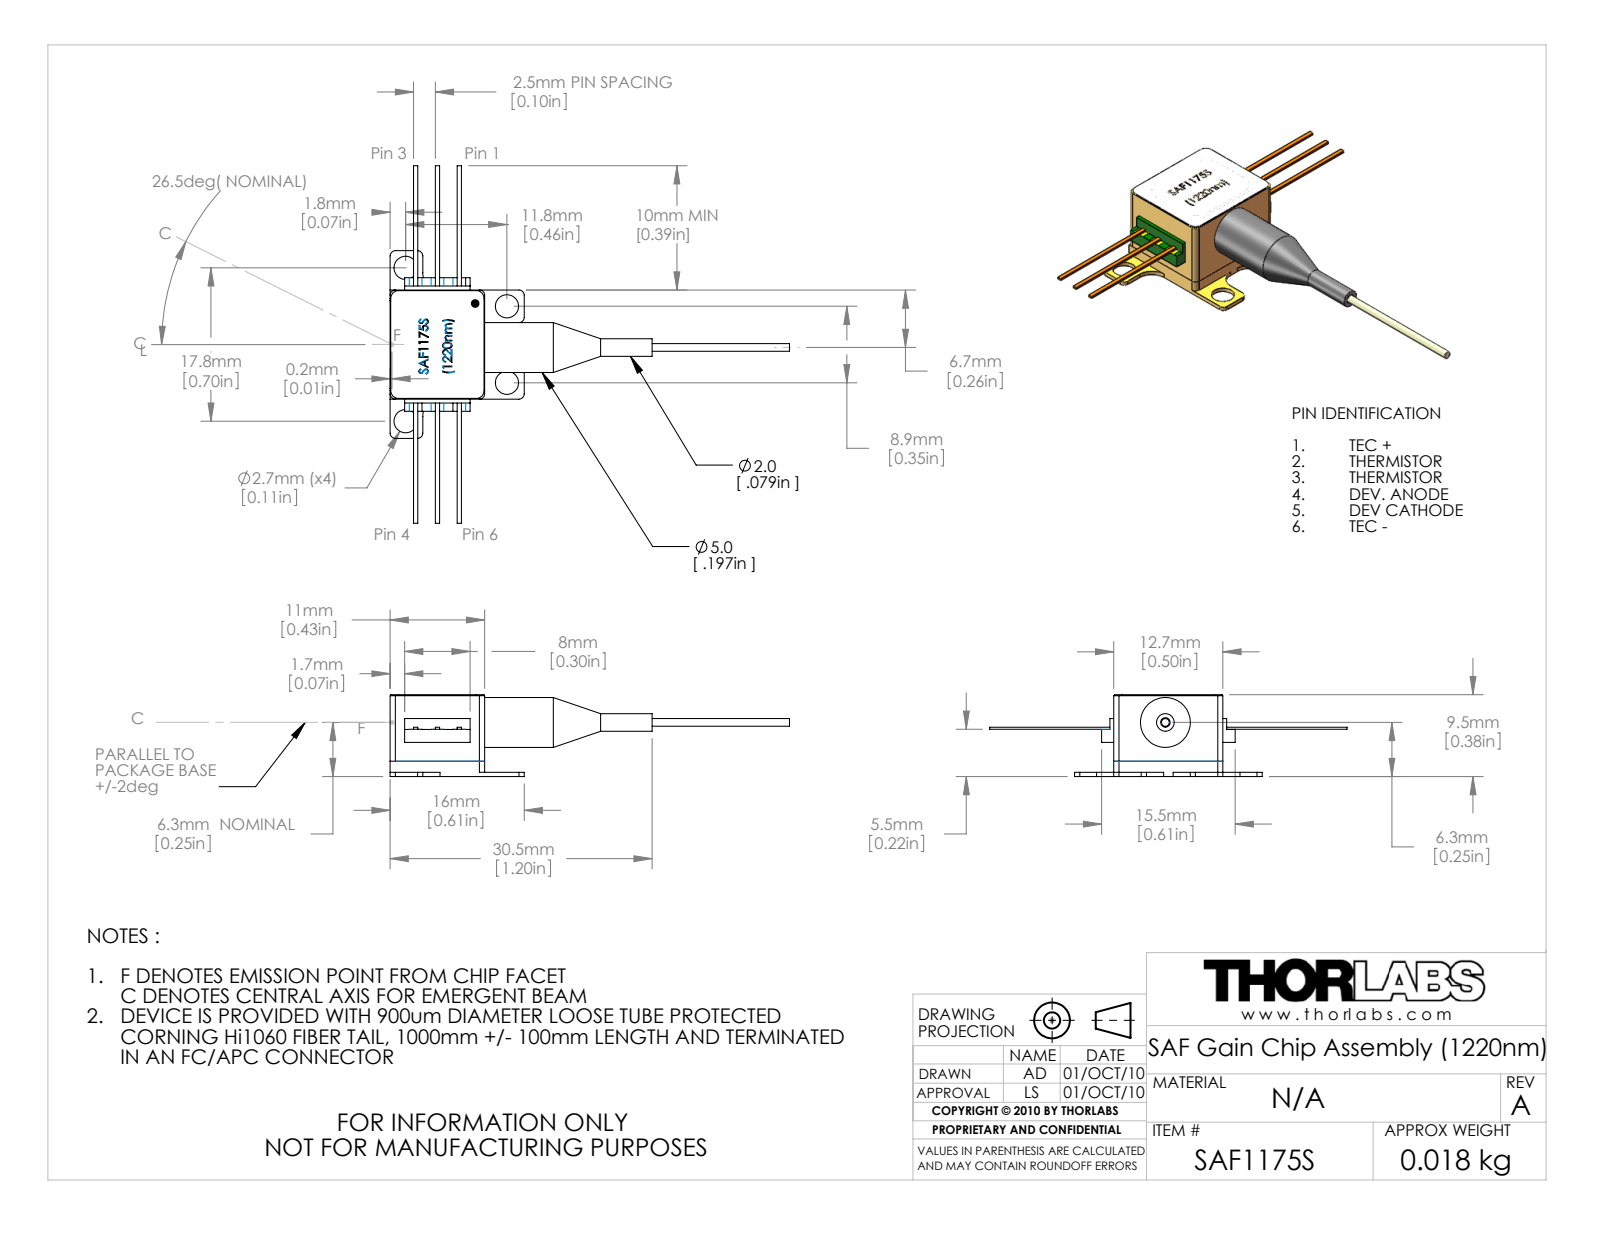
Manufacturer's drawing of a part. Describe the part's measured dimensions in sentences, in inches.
The part is named "21567.E0W". Its 3-D file was written by "SolidWorks 2009 (AUTOMOTIVE_DESIGN)". It is 0 solids with 276 faces: 192 planar, 44 cylindrical and 40 other. Overall it measures 1.831 by 1.638 by 0.375 inches. Round holes: 4 of diameter 0.106, 1 of diameter 0.043. Round bosses or shafts: 1 of diameter 0.228, 1 of diameter 0.08, 1 of diameter 0.035. Partial cylindrical surfaces (rounded edges, fillets, slot ends): 12 of radius 0.024, 4 of radius 0.035, 4 of radius 0.079, 2 of radius 0.012, 2 of radius 0.039, 2 of radius 0.073. The main face-to-face distances are 0.375, 0.37, 0.039, 0.461, 0.307, 0.063, 0.057, 0.36, 0.015, 0.299. The hole center spacings are 0.497, 0.702, 0.35, 0.702.
